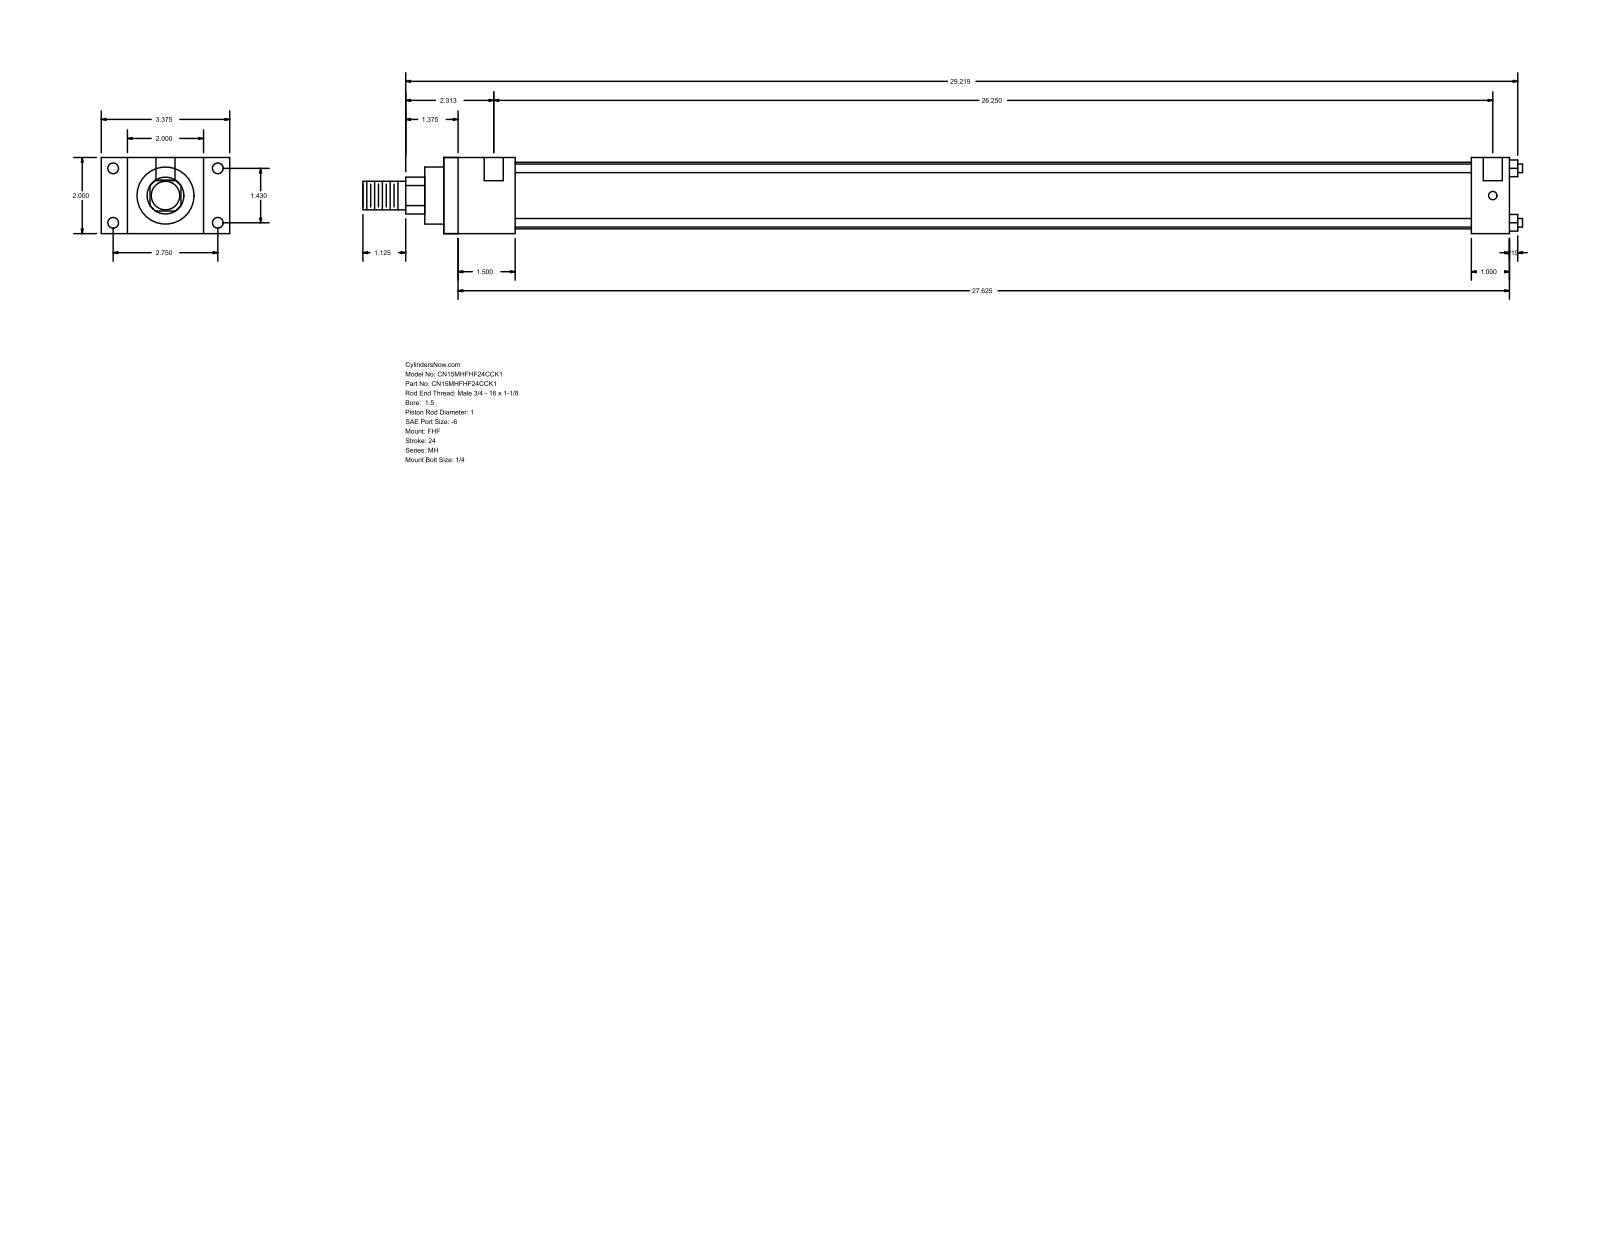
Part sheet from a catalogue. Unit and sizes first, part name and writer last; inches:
Units: inches
Overall size (bounding box): 30.469 × 3.375 × 2
Round holes (diameter × count): ⌀0.219 ×4, ⌀0.281 ×4, ⌀0.5 ×2
Round bosses / shafts (diameter × count): ⌀0.225 ×4, ⌀1.75 ×1, ⌀1.5 ×1, ⌀1 ×1, ⌀0.75 ×1
Partial cylindrical surfaces — rounded edges, fillets, slot ends (radius × count): R0.484 ×1
Main face-to-face distances: 2, 0.687, 2.687, 1.875, 3.375, 28, 26.125, 1, 27, 25.125
Hole centre spacings: 1.43, 2.75, 3.099, 26.375, 0.125, 26.25
Bodies: 0 solids, 88 faces (60 planar, 28 cylindrical, 0 other)
Part name (STEP PRODUCT): MH_FHF__0150_1
STEP written by: GSSL Pune (CONFIG_CONTROL_DESIGN)
